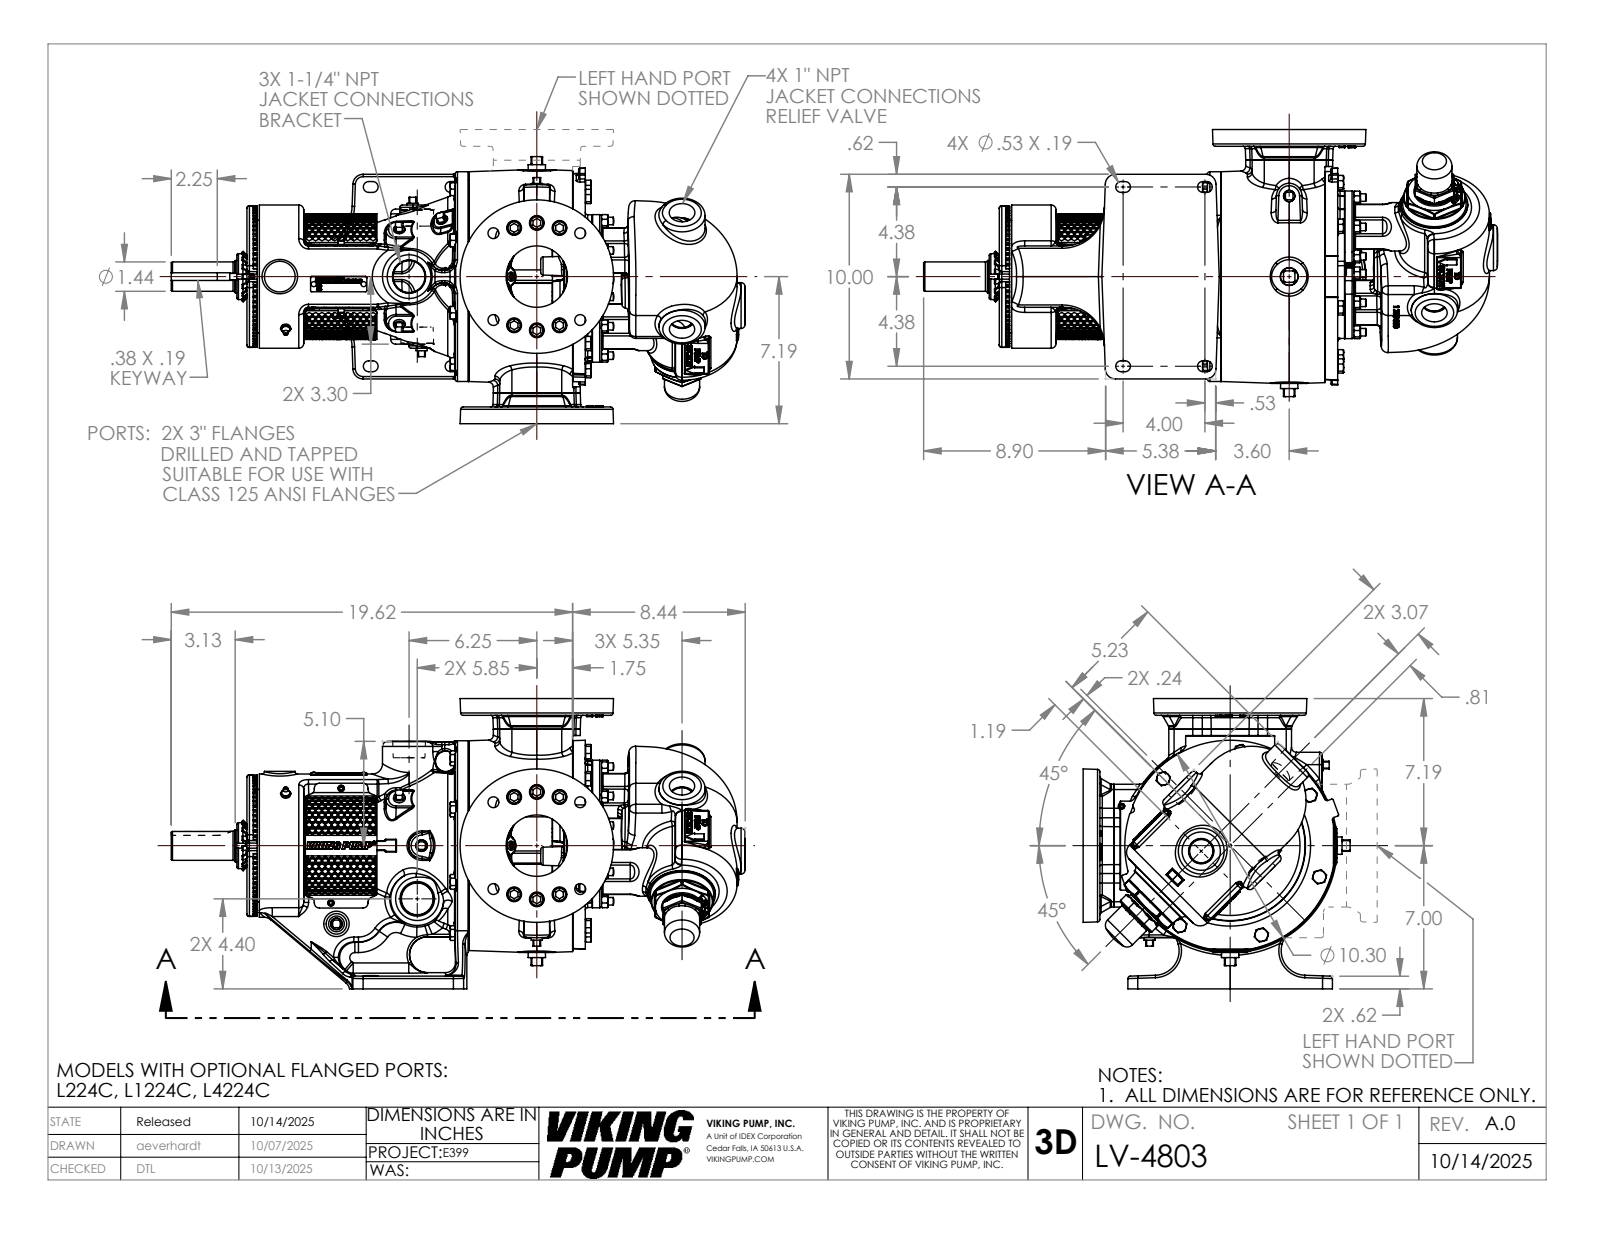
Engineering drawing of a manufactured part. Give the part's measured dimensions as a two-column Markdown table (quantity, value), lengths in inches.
| quantity | value |
| --- | --- |
| part name | LV-4803 |
| STEP written by | SolidWorks 2024 (AUTOMOTIVE_DESIGN) |
| units | inches |
| bodies | 1 solid, 6096 faces (1850 planar, 1063 cylindrical, 3183 other) |
| overall size | 28.059 × 14.188 × 13.053 |
| volume | 1 212 in³ |
| surface area | 1 630 in² |
| round holes (diameter × count) | 0.469 × 12, 0.719 × 12, 0.531 × 8, 1.094 × 8, 0.199 × 6, 0.25 × 6, 0.159 × 3, 0.266 × 2, 0.313 × 2, 3 × 2, 0.453 × 1, 1.577 × 1 |
| round bosses / shafts (diameter × count) | 0.437 × 15, 0.66 × 12, 0.625 × 9, 0.369 × 8, 0.625 × 6, 3.5 × 3, 0.312 × 3, 10.25 × 1 |
| partial cylindrical surfaces (radius × count) | 0.063 × 109, 0.12 × 86, 0.069 × 74, 0.03 × 34, 0.5 × 34, 0.01 × 30, 0.009 × 26, 0.24 × 16 |
| main face-to-face distances | 14.187, 0.82, 2.25, 13.792, 3.537, 10.255, 2.75, 0.5, 2.143, 5.68 |
| hole center spacings | 3, 4.243, 2.625, 1.375, 1.044, 1.136, 2.18, 2.18 |
